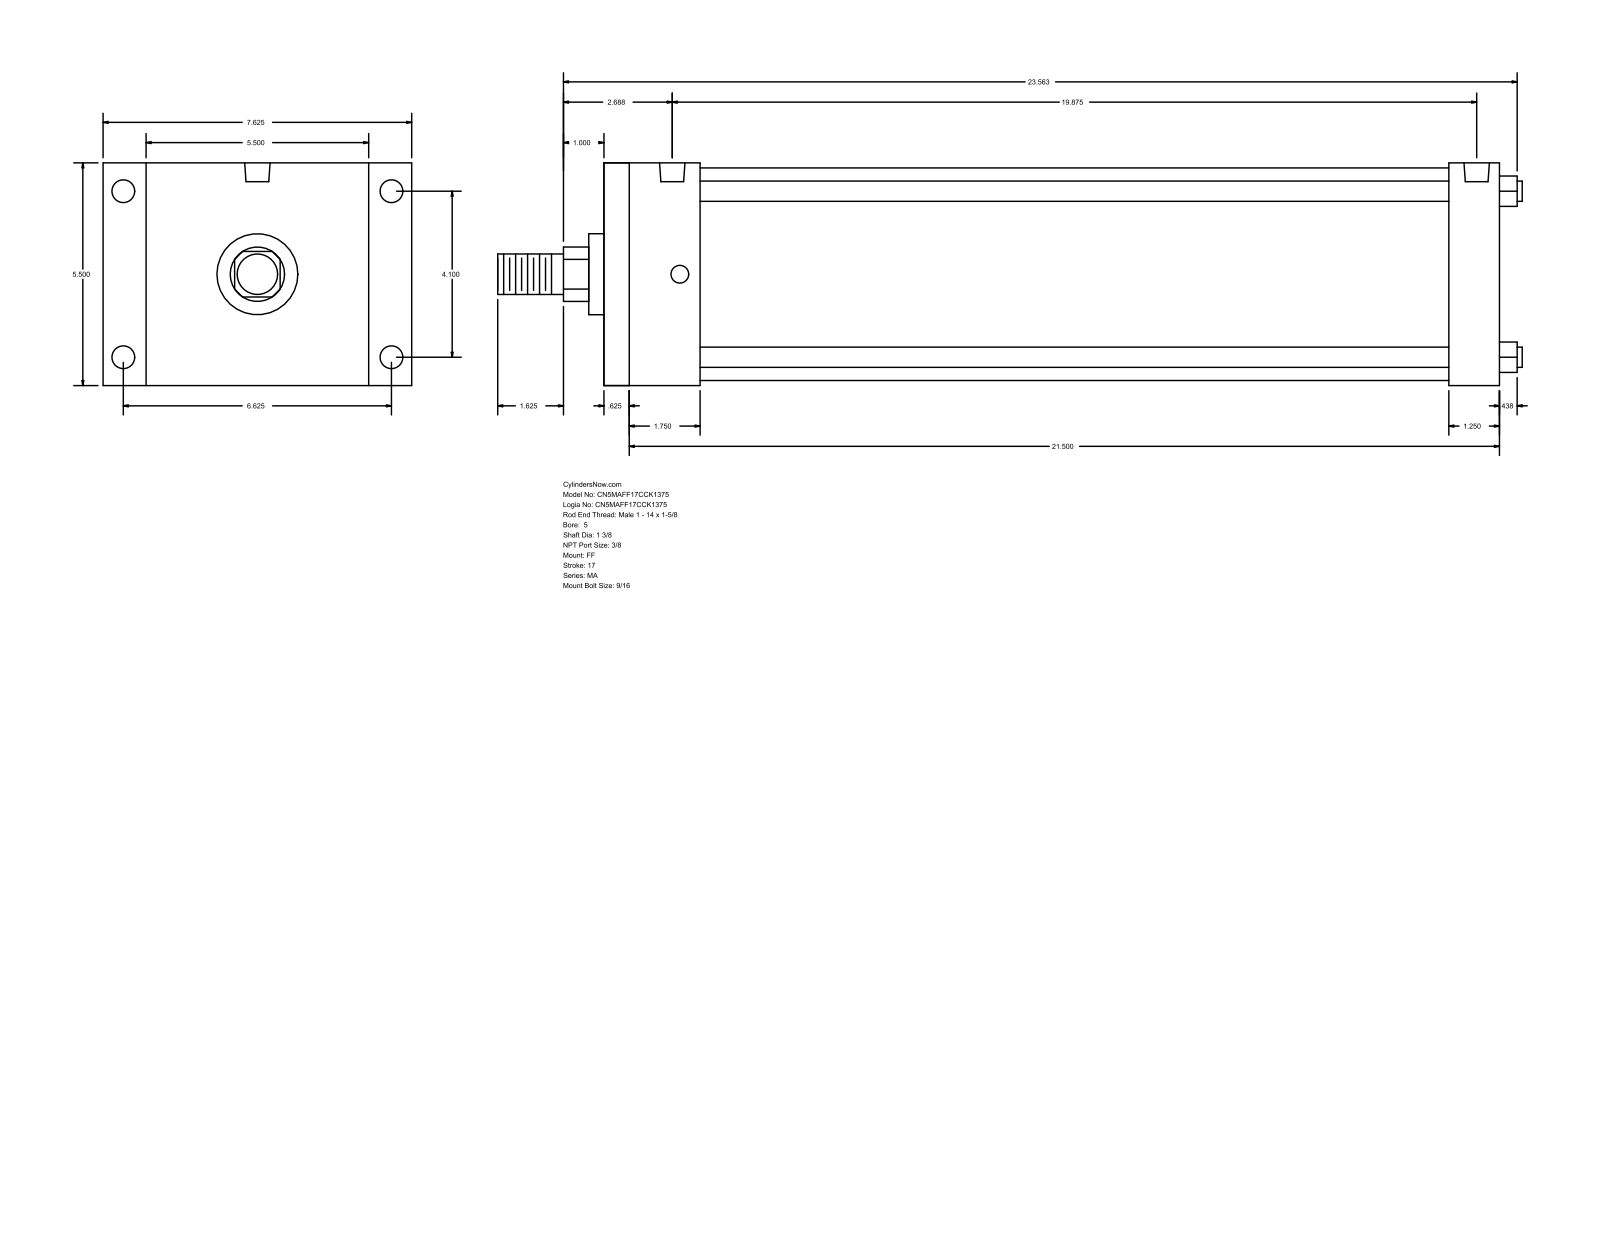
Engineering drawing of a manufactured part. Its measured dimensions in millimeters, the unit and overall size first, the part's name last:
Units: millimetres
Overall size (bounding box): 642.94 × 193.68 × 139.7
Round holes (diameter × count): ⌀11.11 ×4, ⌀14.29 ×4, ⌀15.93 ×2
Round bosses / shafts (diameter × count): ⌀12.7 ×4, ⌀133.35 ×1, ⌀50.8 ×1, ⌀34.92 ×1, ⌀25.4 ×1
Partial cylindrical surfaces — rounded edges, fillets, slot ends (radius × count): R17.06 ×1
Main face-to-face distances: 139.7, 561.98, 15.87, 546.11, 530.22, 514.35, 31.76, 60.32, 44.45, 469.9
Hole centre spacings: 104.14, 168.28, 197.9, 495.3, 4.76, 4.77, 500.06, 500.07
Bodies: 0 solids, 92 faces (64 planar, 28 cylindrical, 0 other)
Part name (STEP PRODUCT): MA_FF__0500_1.375
STEP written by: GSSL Pune (CONFIG_CONTROL_DESIGN)
